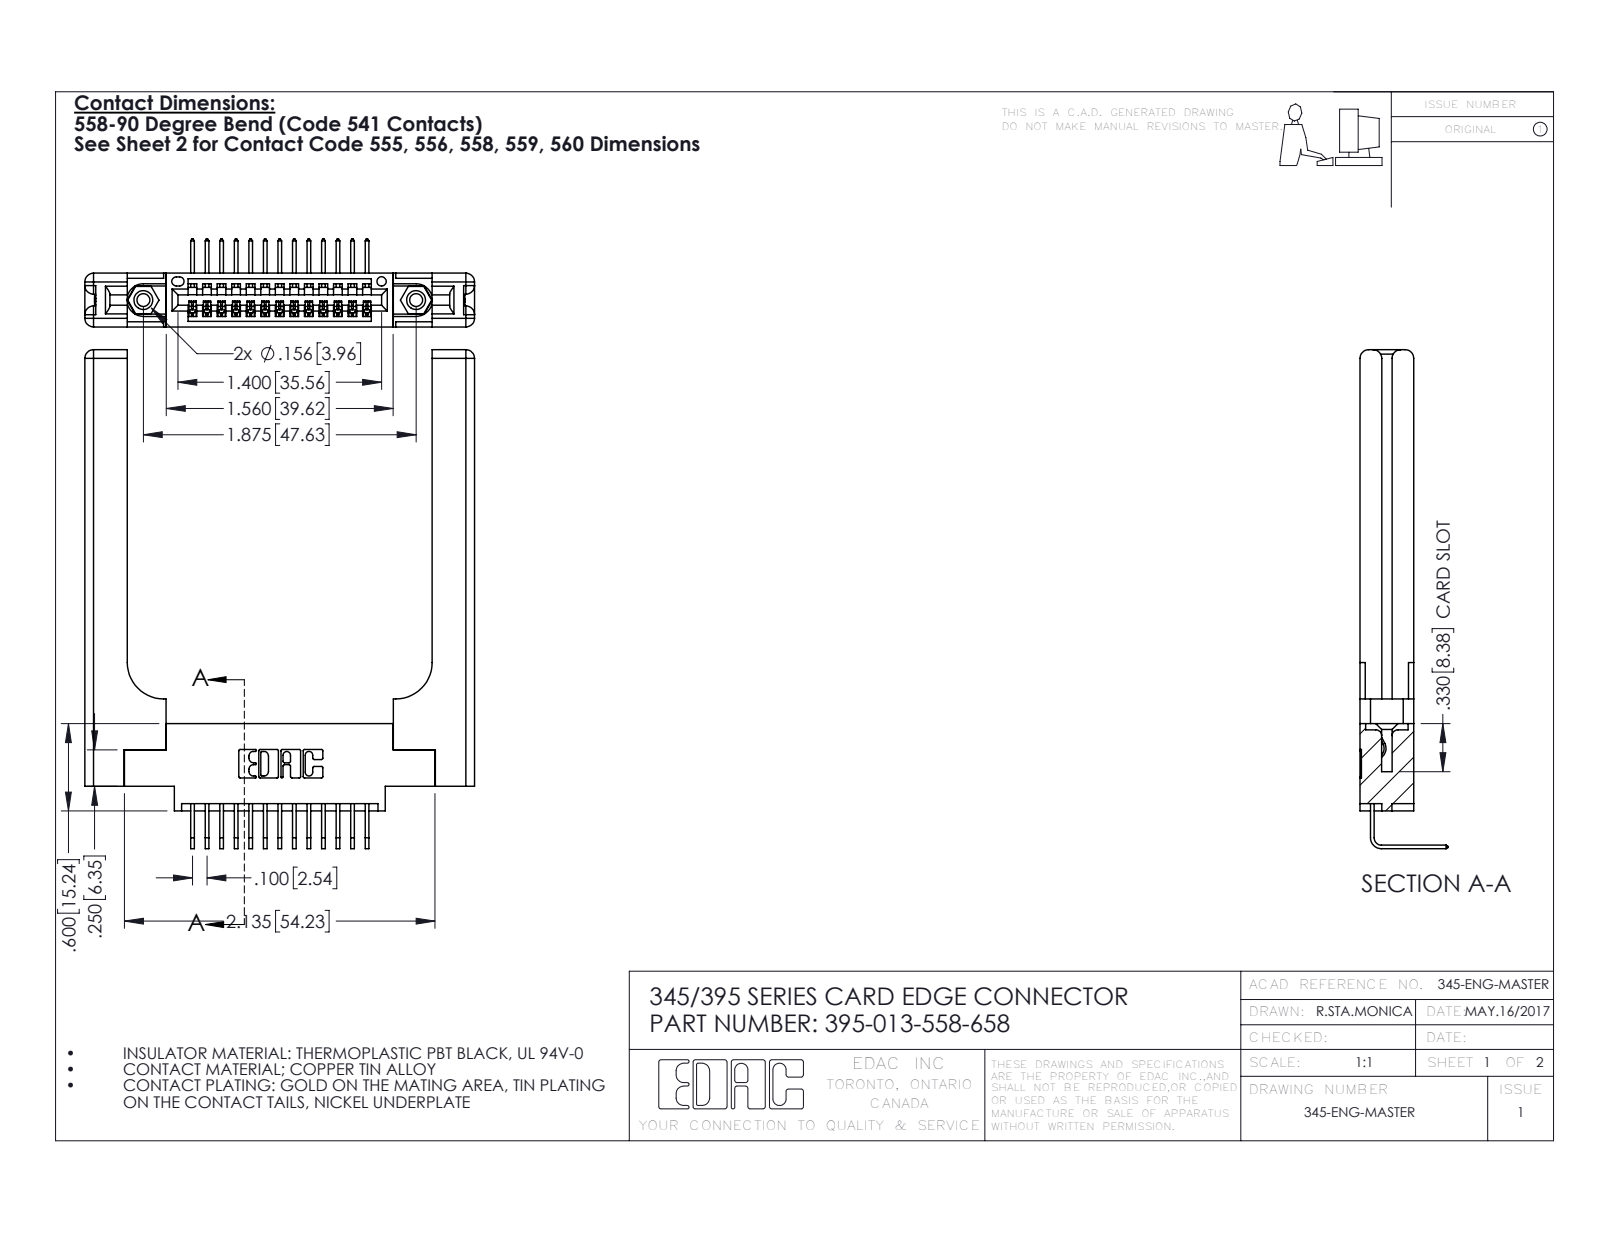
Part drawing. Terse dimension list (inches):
name: 345-292-001_558 Tail - 2; 395-013-558-658; 345-220-058_345-220-058; 345-250-001_345-250-001-102 (+1 more)
written by: SolidWorks 2016 (CONFIG_CONTROL_DESIGN)
unit: in
bodies: 18 solids, 1166 faces (778 planar, 328 cylindrical, 60 other)
size: 3.429 × 2.679 × 0.605
volume: 0.895 in³; area: 20.88 in²
holes: 2× ⌀0.089, 2× ⌀0.125, 2× ⌀0.156, 1× ⌀0.064
bosses: 2× ⌀0.155
rounds: 26× R0.006, 22× R0.01, 16× R0.06, 6× R0.007, 6× R0.031, 3× R0.026, 2× R0.03, 2× R0.031
face distances: 0.37, 0.072, 0.15, 0.298, 0.148, 0.077, 0.22, 0.12, 2.096, 0.123
hole spacings: 0.27, 1.643, 1.875
